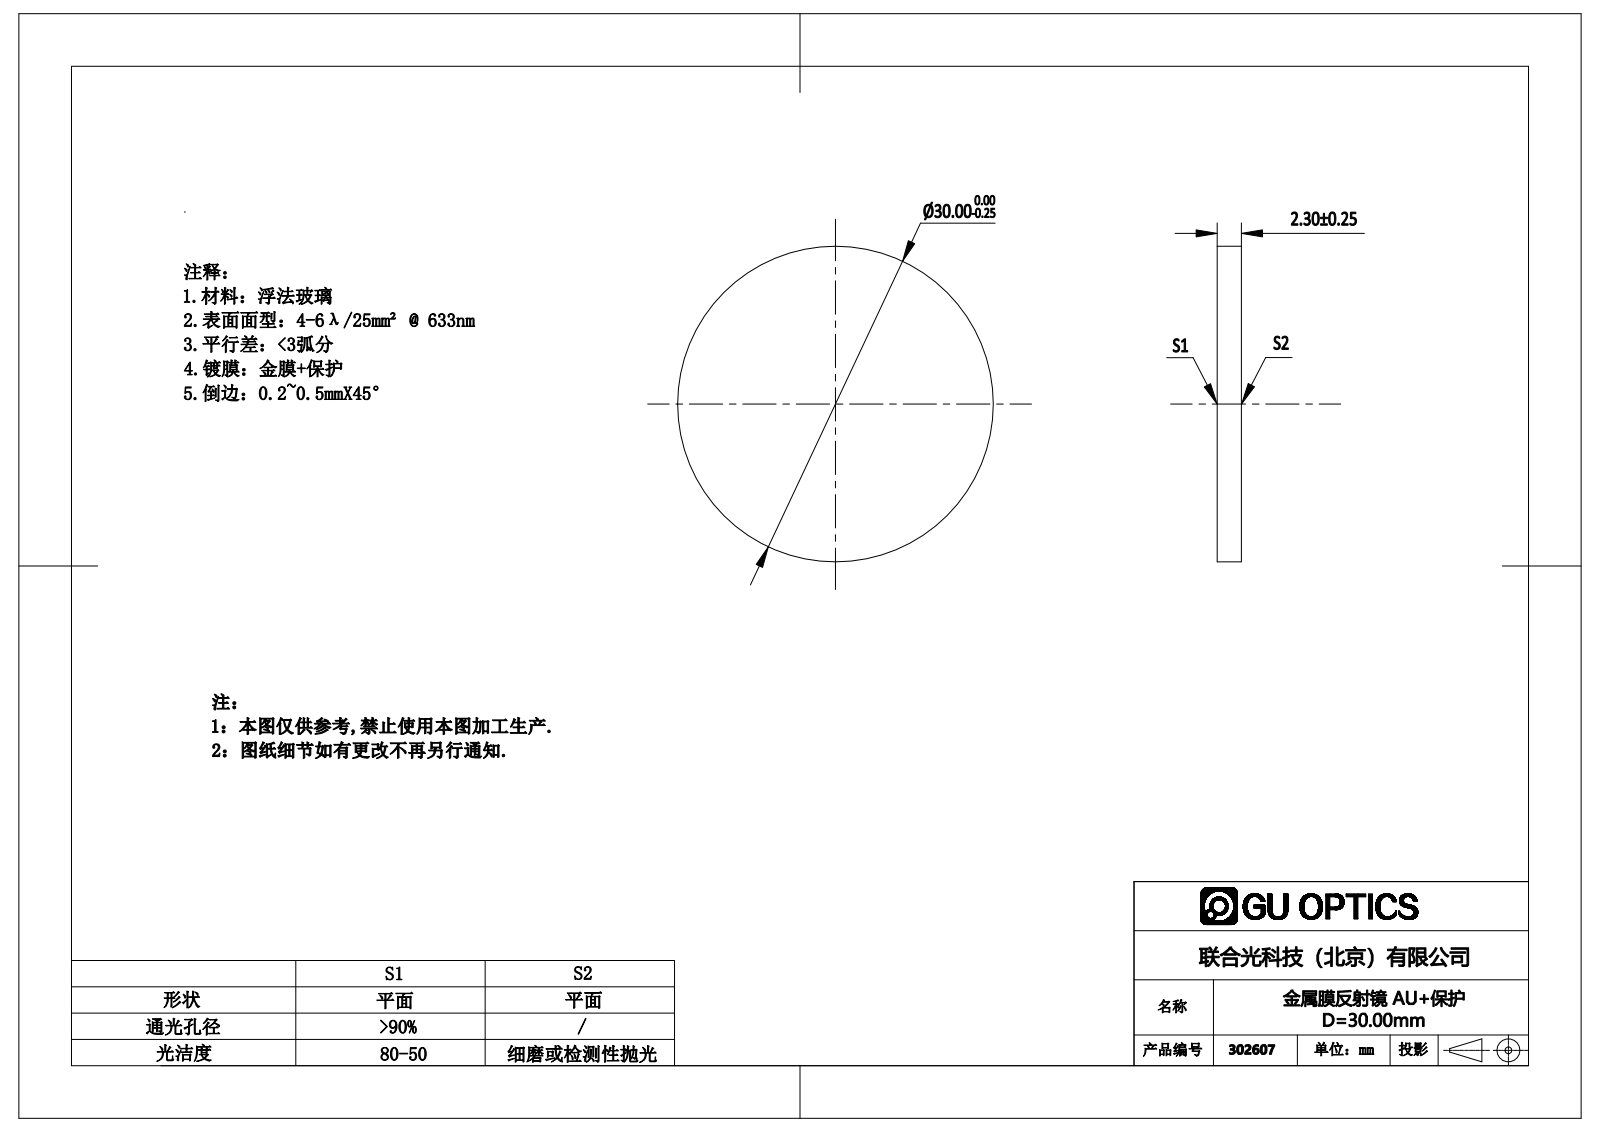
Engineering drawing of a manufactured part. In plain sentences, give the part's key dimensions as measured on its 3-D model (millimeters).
The part is named "302520". Its 3-D file was written by "SolidWorks 2016 (AUTOMOTIVE_DESIGN)". It is 1 solid with 4 faces: 2 planar, 2 cylindrical and 0 other. Overall it measures 30 by 30 by 2.3 millimeters. Its volume is 1 626 cubic millimeters and its surface area 1 630 square millimeters. Round bosses or shafts: 1 of diameter 30. The main face-to-face distances are 2.3.
